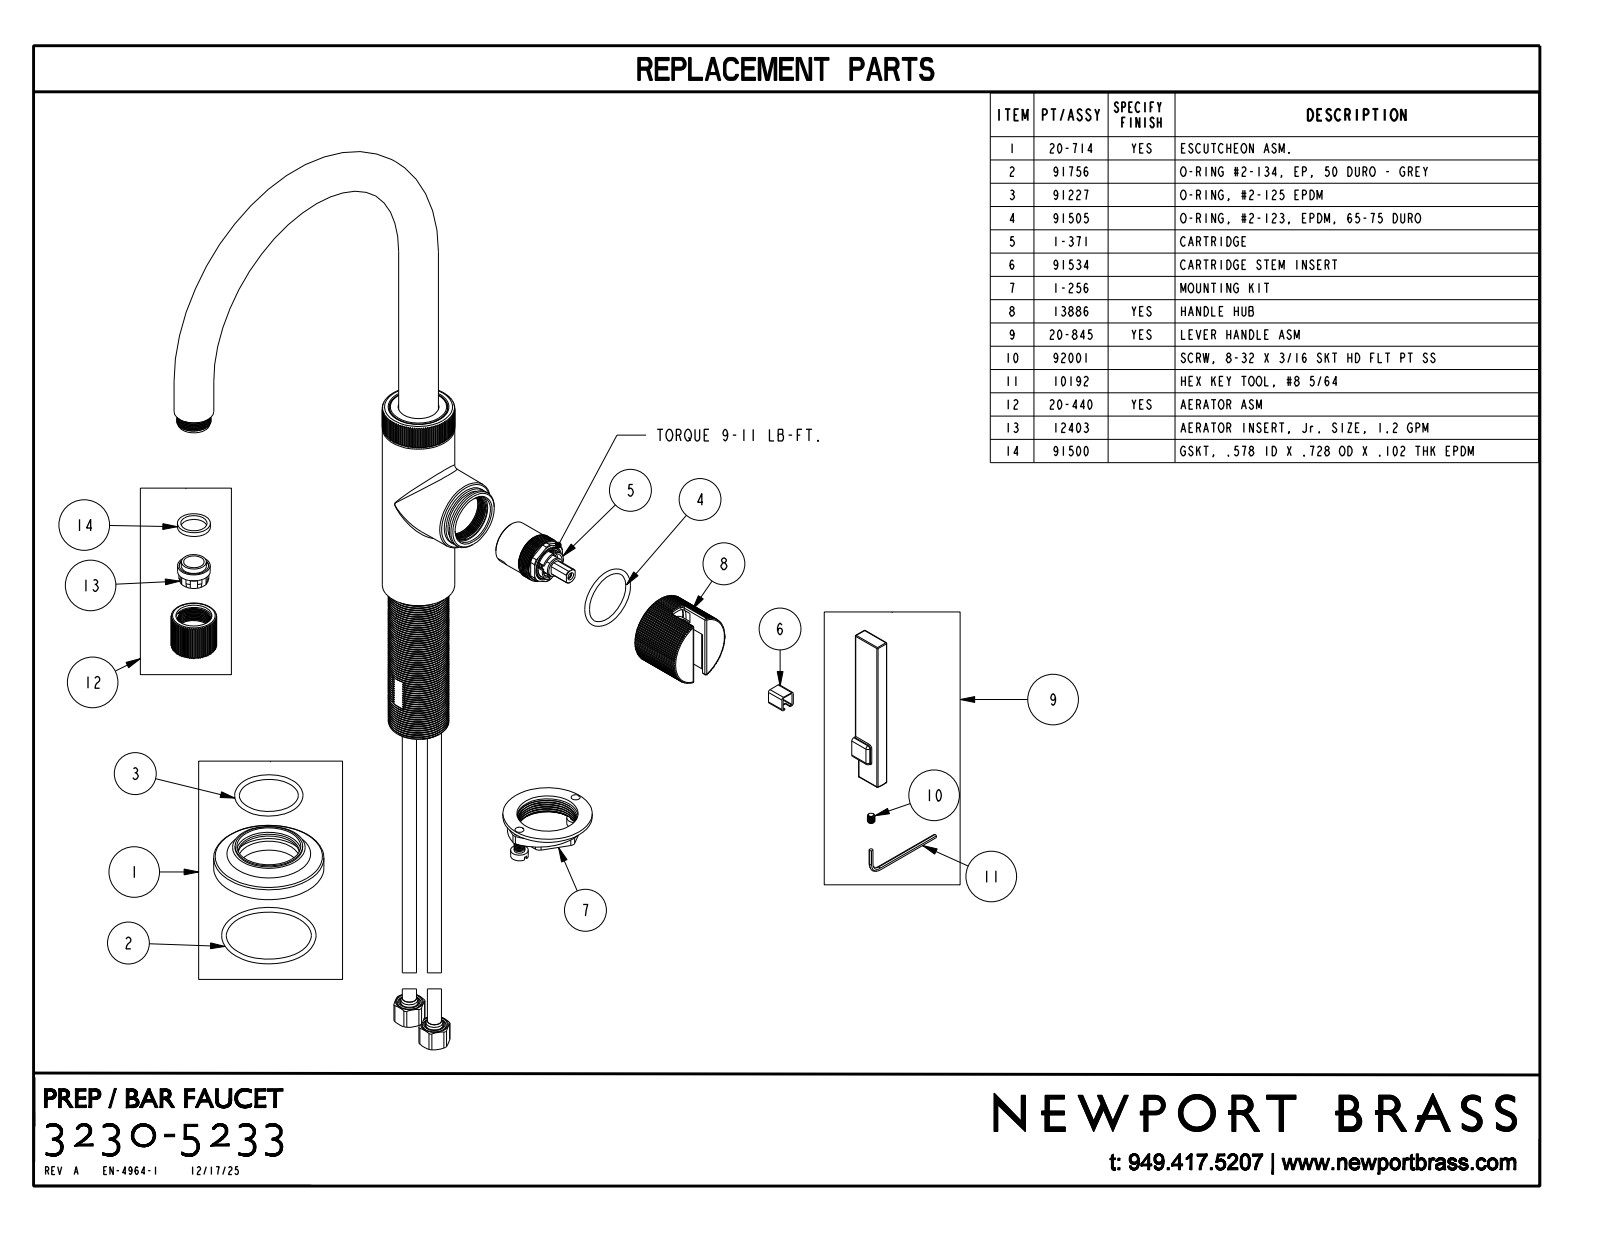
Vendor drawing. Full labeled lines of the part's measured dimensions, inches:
Part name (STEP PRODUCT): 3230-5233
STEP written by: CREO PARAMETRIC BY PTC INC, 2023134 (CONFIG_CONTROL_DESIGN)
Units: inches
Bodies: 3 solids, 1125 faces (627 planar, 405 cylindrical, 93 other)
Overall size (bounding box): 13.475 × 8.715 × 3.977
Volume: 24.89 in³ · Surface area: 120.2 in²
Round holes (diameter × count): ⌀0.56 ×1, ⌀0.62 ×1, ⌀0.691 ×1, ⌀1.093 ×1, ⌀1.1 ×1, ⌀1.3 ×1, ⌀1.35 ×1, ⌀1.394 ×1, ⌀1.43 ×1
Round bosses / shafts (diameter × count): ⌀0.875 ×2, ⌀2.43 ×1, ⌀1.6 ×1, ⌀1.354 ×1, ⌀1.234 ×1, ⌀0.466 ×1
Partial cylindrical surfaces — rounded edges, fillets, slot ends (radius × count): R0.02 ×19, R0.03 ×10, R0.01 ×8, R0.06 ×8, R0.13 ×6, R0.04 ×4, R0.05 ×2, R0.79 ×2
Main face-to-face distances: 0.3, 0.7, 0.705, 0.452, 1.152, 1.157, 0.489, 0.663, 0.211, 0.494
Hole centre spacings: 7
